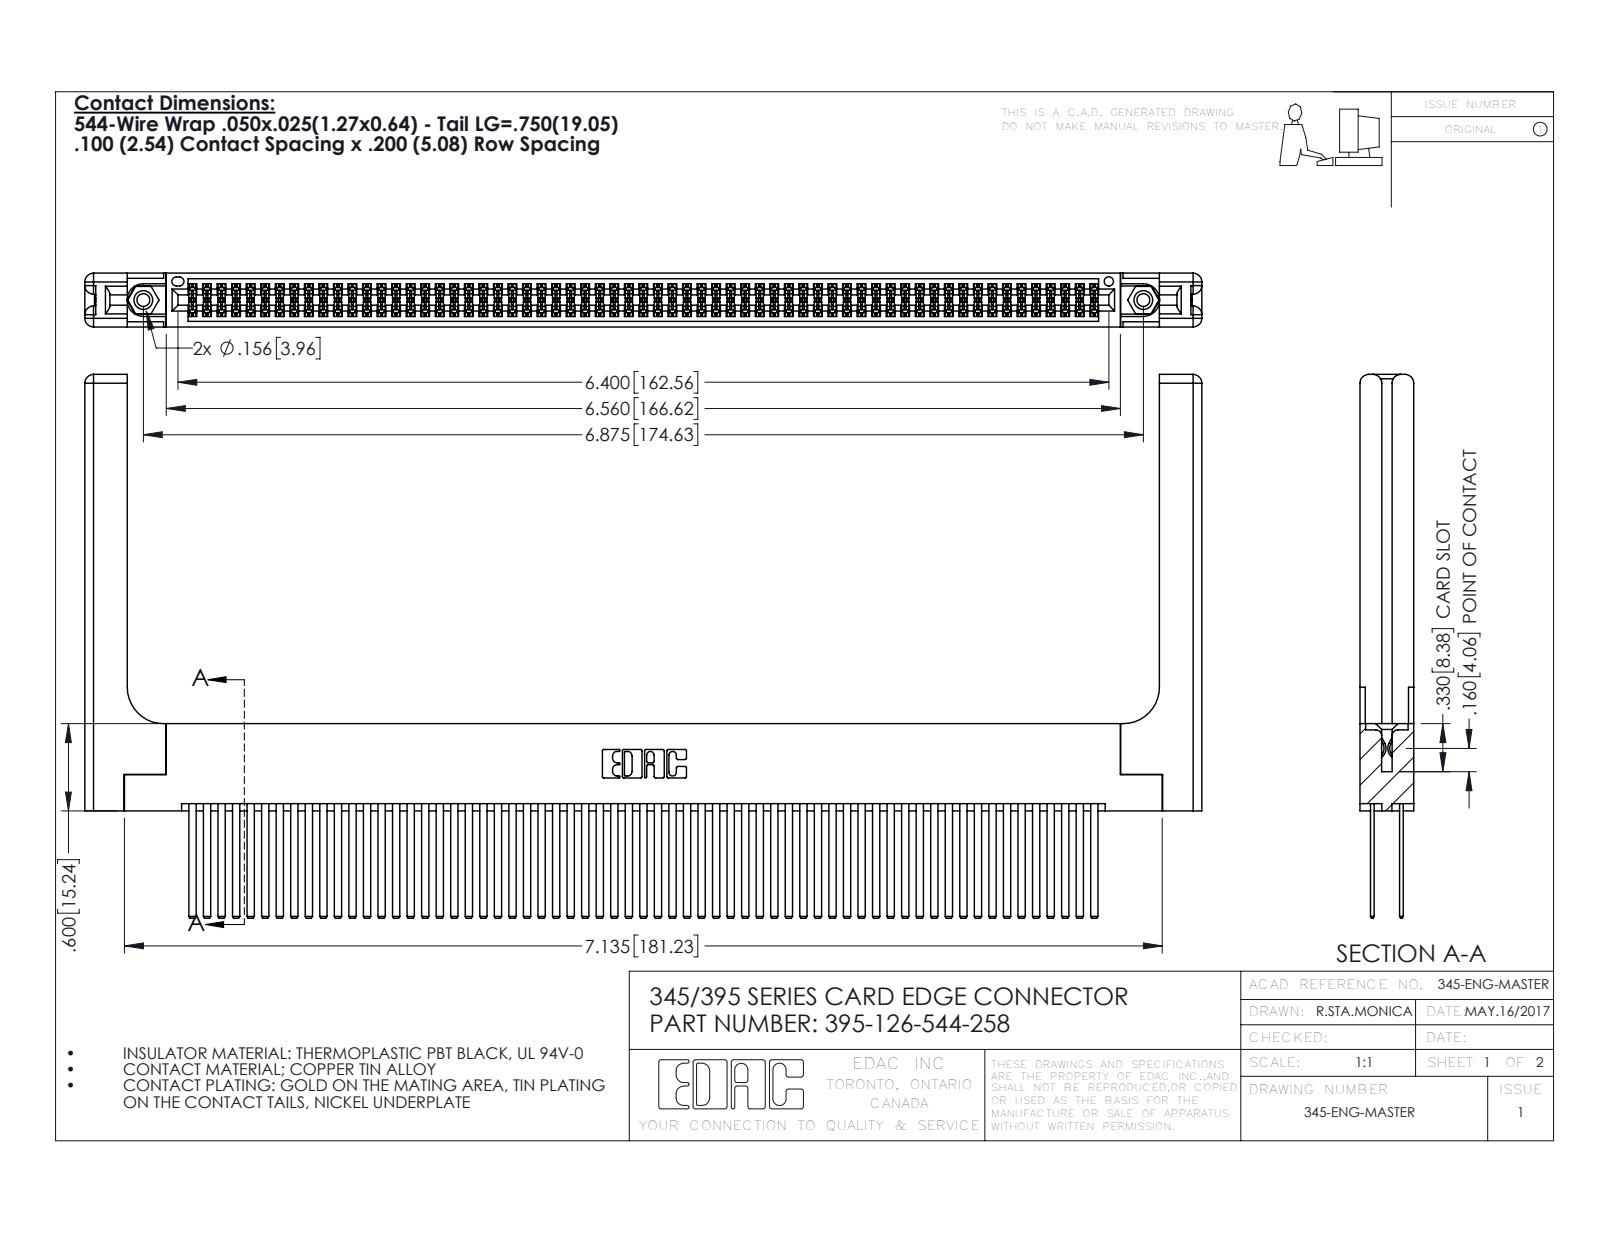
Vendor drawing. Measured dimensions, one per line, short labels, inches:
name: 345-250-001_345-250-001-102; 345-292-001_345-293-144; 345-220-058_345-220-058; 395-126-544-258 (+1 more)
written by: SolidWorks 2016 (CONFIG_CONTROL_DESIGN)
unit: in
bodies: 131 solids, 5926 faces (3882 planar, 1984 cylindrical, 60 other)
size: 7.679 × 3.737 × 0.37
volume: 1.793 in³; area: 64.4 in²
holes: 2× ⌀0.089, 2× ⌀0.125, 2× ⌀0.156, 1× ⌀0.064
bosses: 2× ⌀0.155
rounds: 189× R0.006, 22× R0.01, 16× R0.06, 6× R0.007, 6× R0.031, 3× R0.026, 2× R0.014, 2× R0.019
face distances: 0.072, 0.298, 0.2, 0.098, 0.272, 0.025, 0.225, 0.37, 0.175, 0.148
hole spacings: 0.27, 6.639, 6.875
